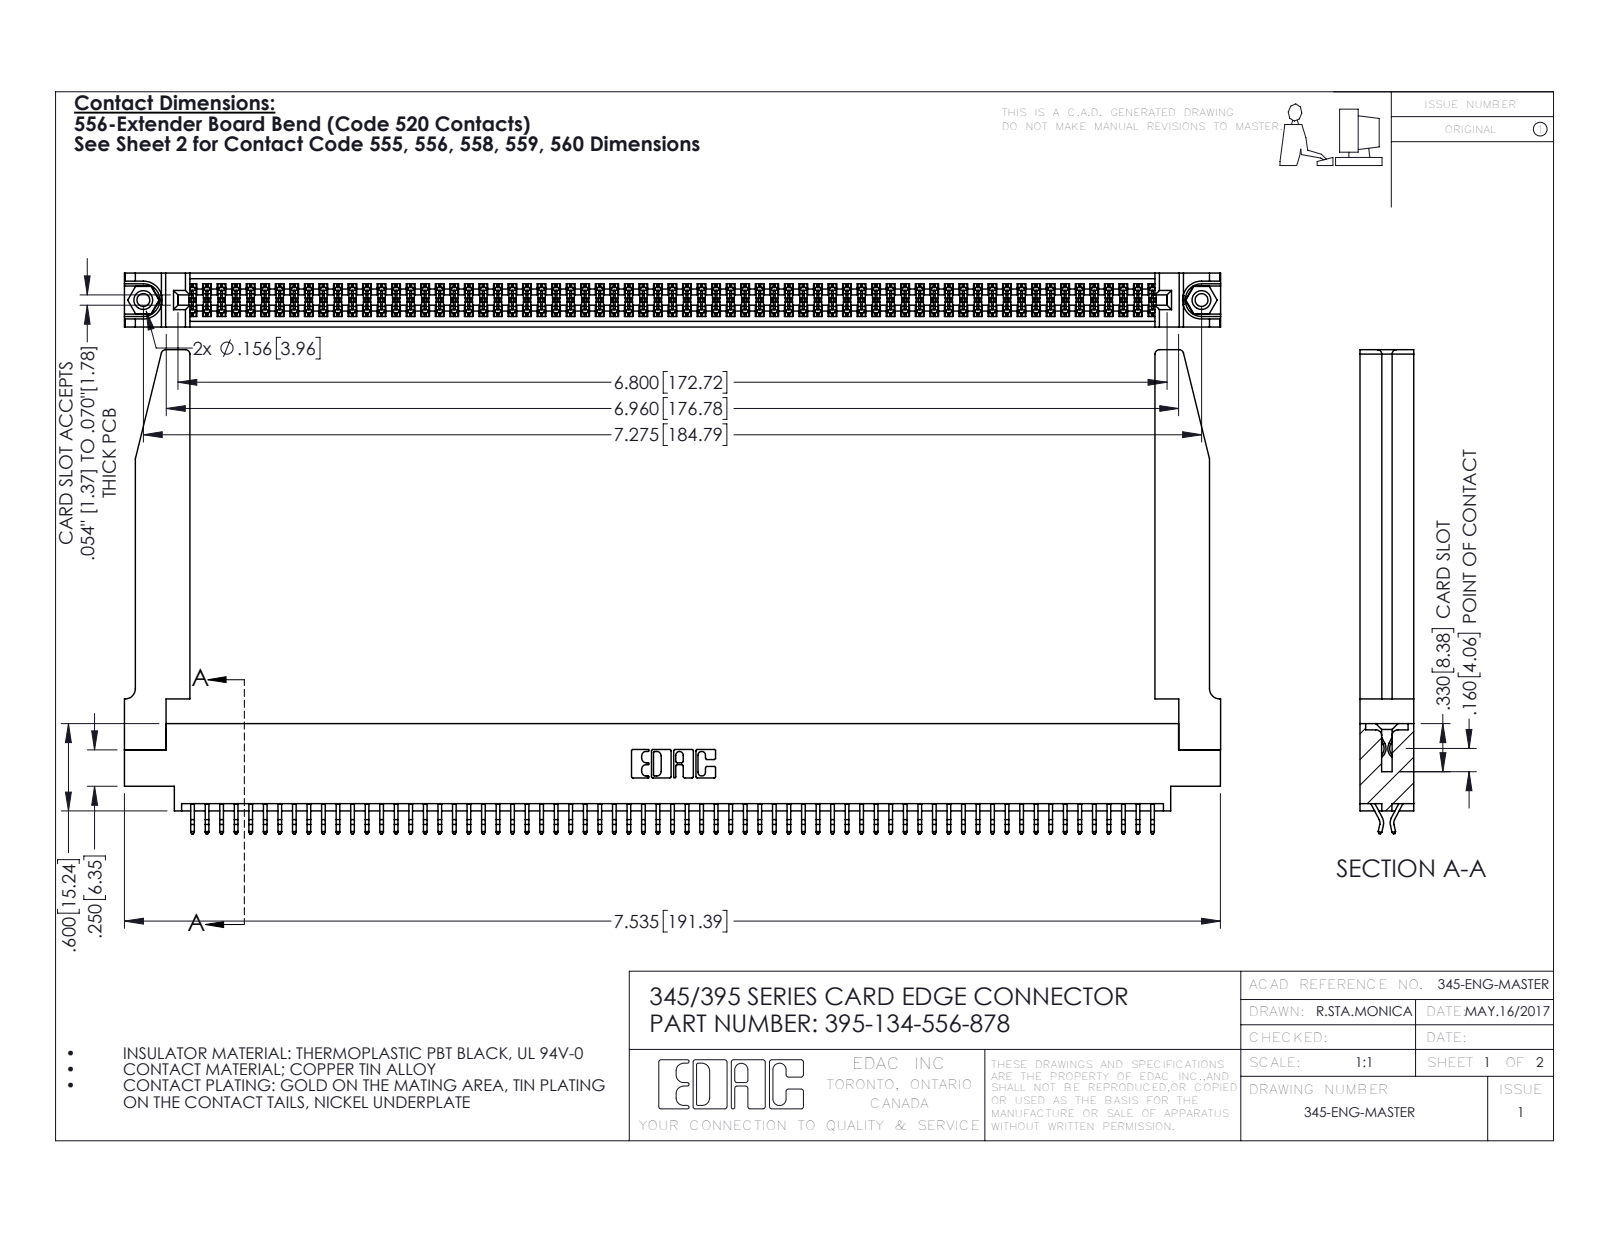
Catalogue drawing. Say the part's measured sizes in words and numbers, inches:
The part is named "345-220-078_345-220-078; 345 Part_0.170 Offset - 0.156 Dia-TH; 345-250-001_345-250-001-102; 345-292-001_556 Tail (+1 more)". Its 3-D file was written by "SolidWorks 2016 (CONFIG_CONTROL_DESIGN)". It is 139 solids with 7868 faces: 5184 planar, 2632 cylindrical and 52 other. Overall it measures 7.536 by 3.327 by 0.37 inches. Its volume is 1.616 cubic inches and its surface area 54.25 square inches. Round holes: 2 of diameter 0.089, 2 of diameter 0.125, 2 of diameter 0.156, 1 of diameter 0.064. Round bosses or shafts: 2 of diameter 0.155. Partial cylindrical surfaces (rounded edges, fillets, slot ends): 201 of radius 0.006, 22 of radius 0.01, 8 of radius 0.03, 6 of radius 0.007, 6 of radius 0.031, 3 of radius 0.026, 2 of radius 0.01, 2 of radius 0.014. The main face-to-face distances are 0.072, 0.37, 0.298, 0.025, 0.098, 0.272, 0.2, 0.225, 0.175, 0.149. The hole center spacings are 0.27, 7.039, 7.275.
